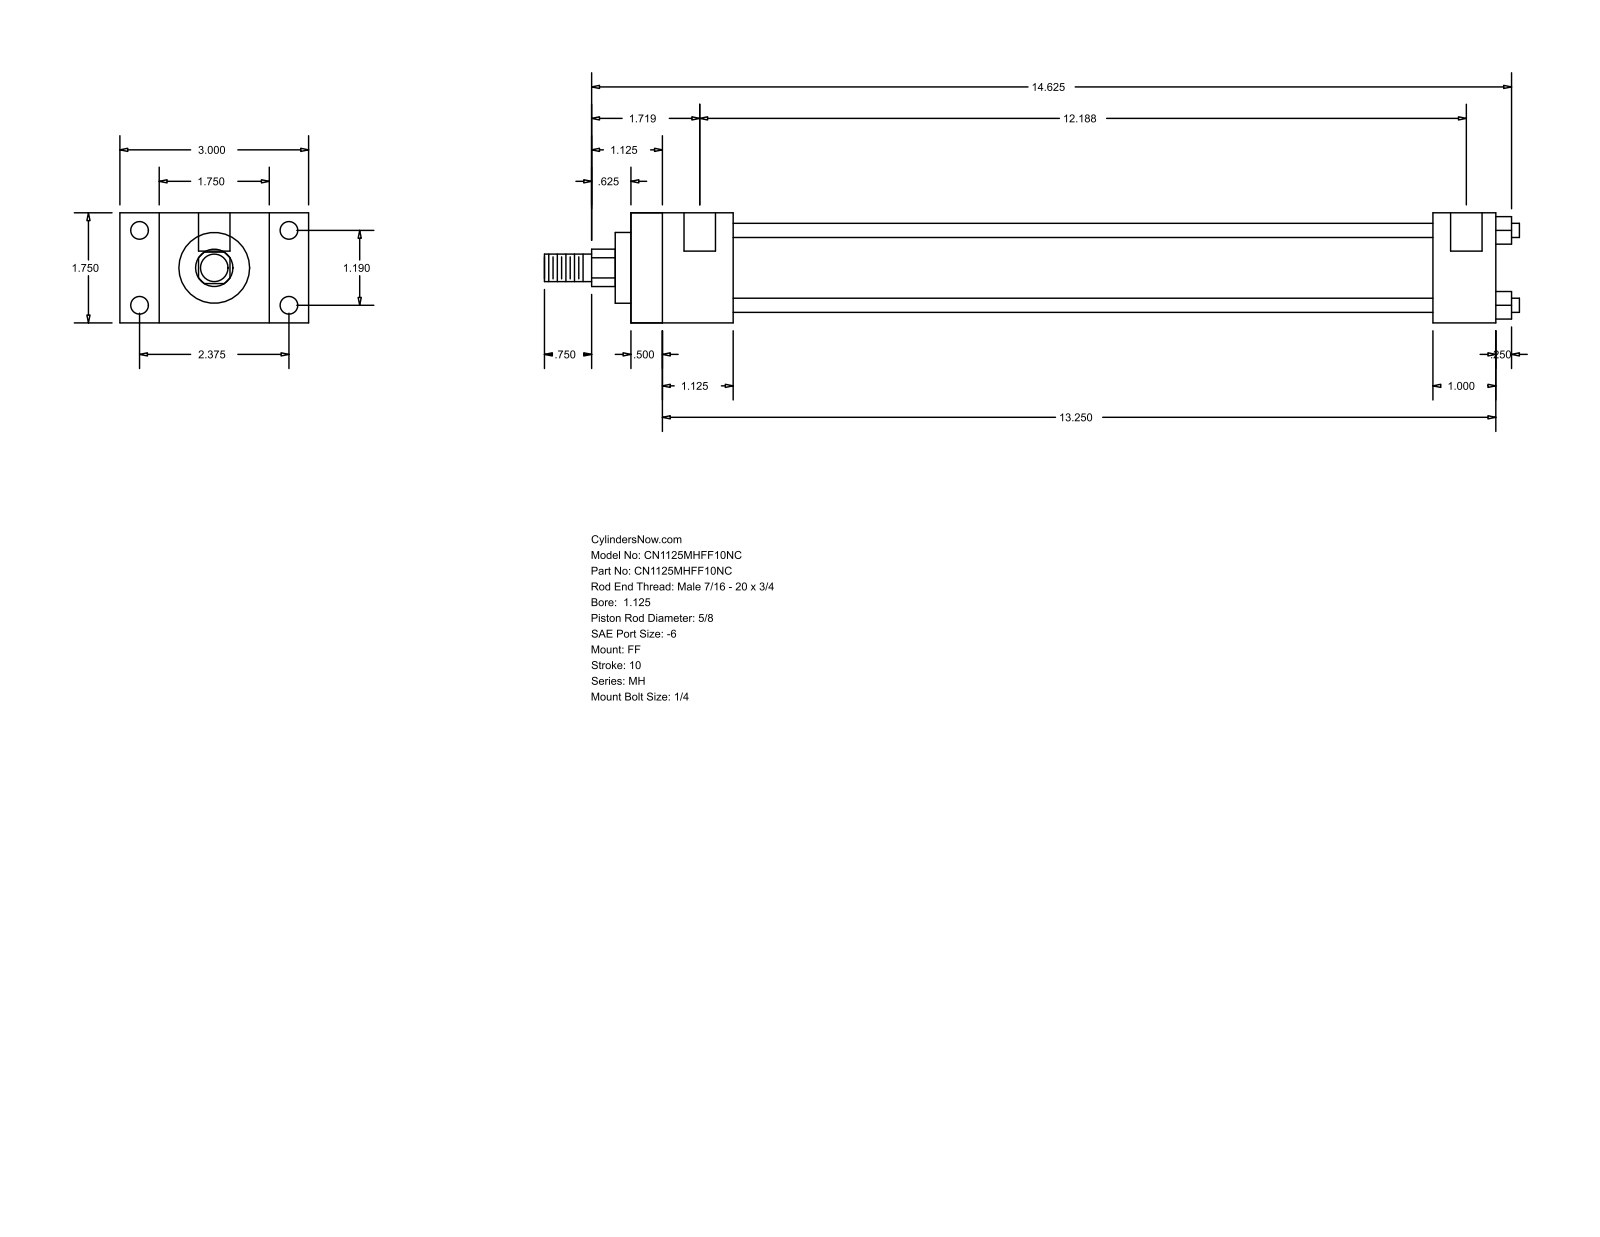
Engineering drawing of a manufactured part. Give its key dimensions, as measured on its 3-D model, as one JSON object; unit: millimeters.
{"part_name": "MH_FF__0112_0.625", "step_written_by": "GSSL Pune (CONFIG_CONTROL_DESIGN)", "units": "millimeters", "bodies": {"solids": 0, "faces": 92, "planar": 64, "cylindrical": 28, "other": 0}, "overall_size": [393.7, 76.2, 44.45], "round_holes": [[5.56, 4], [7.14, 4], [12.7, 2]], "round_bosses_or_shafts": [[5.71, 4], [34.92, 1], [28.57, 1], [15.88, 1], [11.11, 1]], "partial_cylinders_radius": [[7.54, 1]], "face_to_face_distances": [44.46, 349.24, 15.87, 12.69, 336.55, 28.58, 60.33, 41.27, 323.85, 311.16], "hole_center_spacings": [30.22, 60.32, 67.47, 306.39, 3.17, 309.56]}
